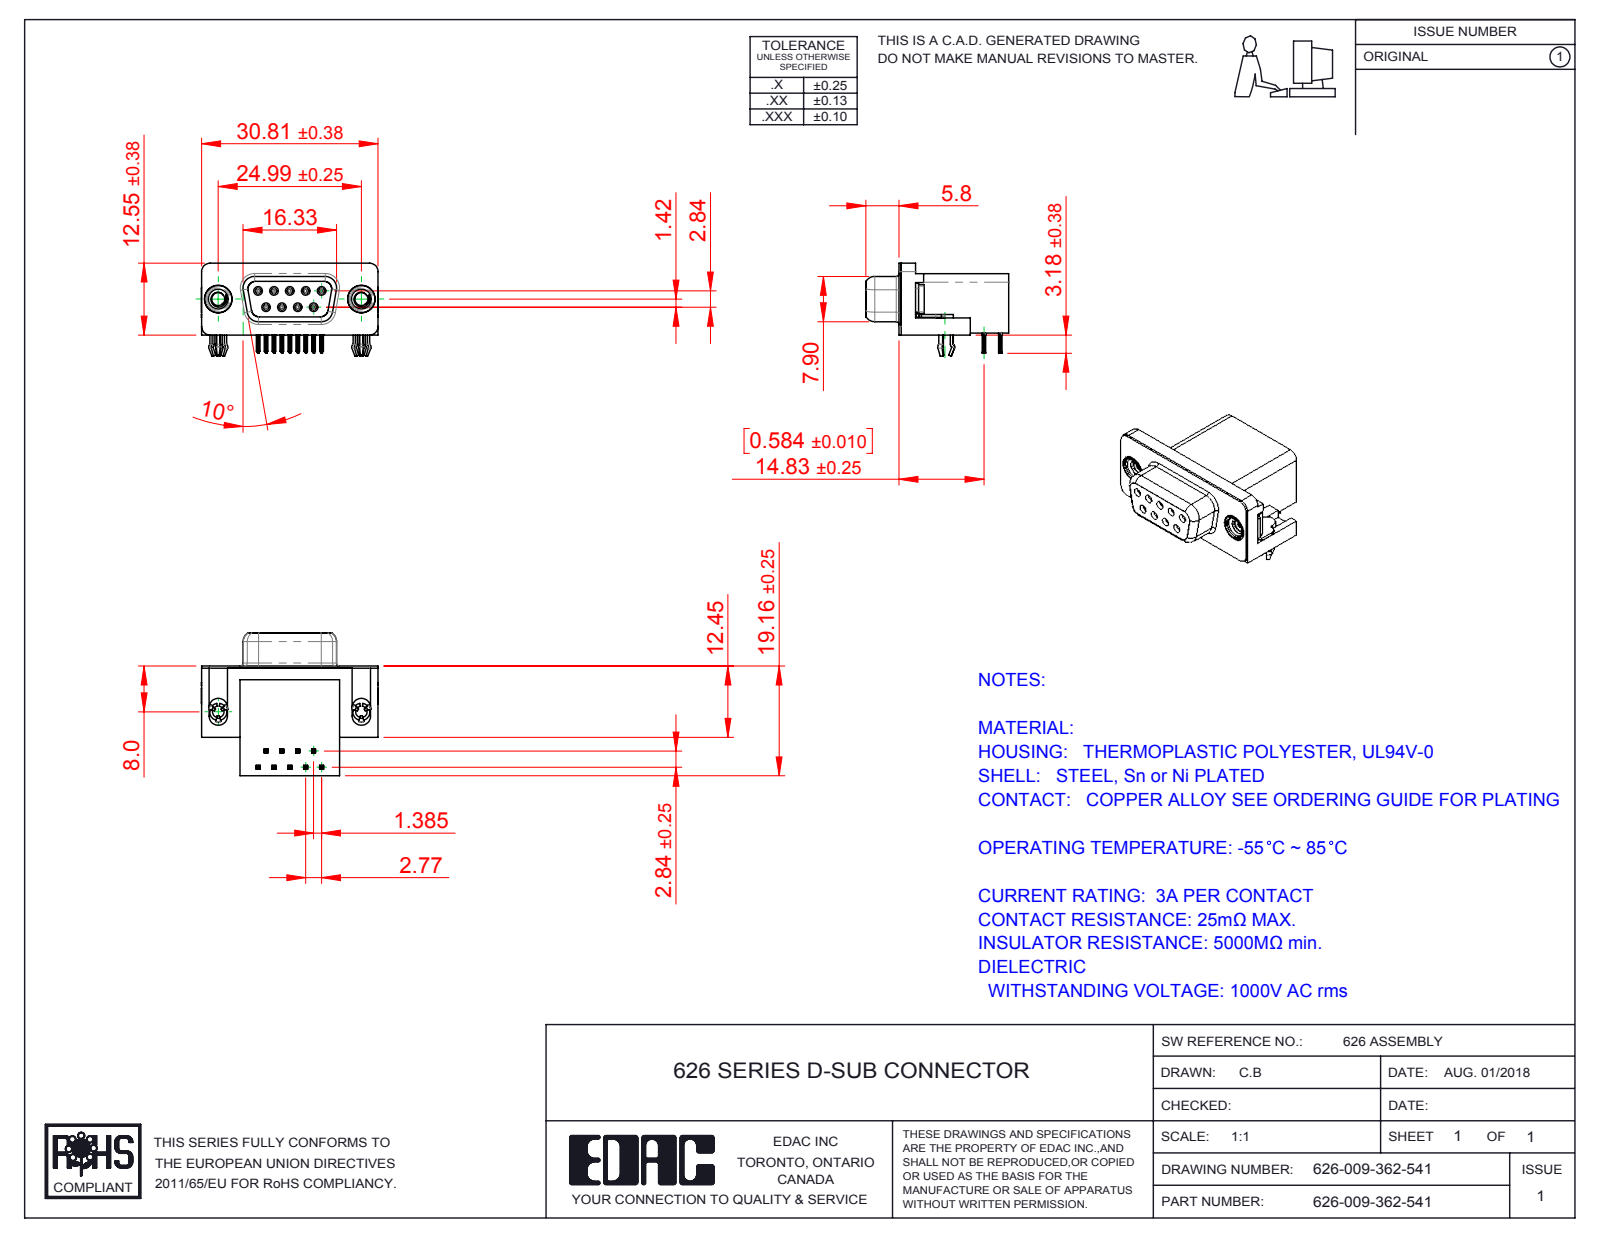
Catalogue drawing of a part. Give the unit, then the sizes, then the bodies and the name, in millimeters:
Units: millimetres
Overall size (bounding box): 30.89 × 24.96 × 16.25
Round holes (diameter × count): ⌀0.8 ×9, ⌀0.9 ×9, ⌀2 ×2, ⌀2.26 ×2, ⌀4 ×2, ⌀4.8 ×2, ⌀5 ×2
Round bosses / shafts (diameter × count): ⌀1.2 ×9, ⌀4.9 ×2, ⌀4.75 ×2, ⌀3.9 ×2, ⌀3 ×2
Partial cylindrical surfaces — rounded edges, fillets, slot ends (radius × count): R0.1 ×72, R0.15 ×36, R0.35 ×18, R1 ×18, R0.25 ×12, R0.34 ×9, R1.35 ×8, R1.6 ×8
Main face-to-face distances: 0.4, 10.34, 0.35, 18.76, 19.16, 2.9, 2.5, 6.2, 16.26, 10.69
Hole centre spacings: 3.16, 2.77, 5.54, 5.03, 5.04, 8.31, 7.48, 7.49
Volume: 4 978 mm³ · Surface area: 5 852 mm²
Bodies: 15 solids, 1676 faces (722 planar, 422 cylindrical, 532 other)
Part name (STEP PRODUCT): 626 Contact Bottom; 626 4-40 Threaded Rivet; 626 3 Prong Board Lock; 626 Contact Top (+3 more)
STEP written by: SolidWorks 2016 (CONFIG_CONTROL_DESIGN)
